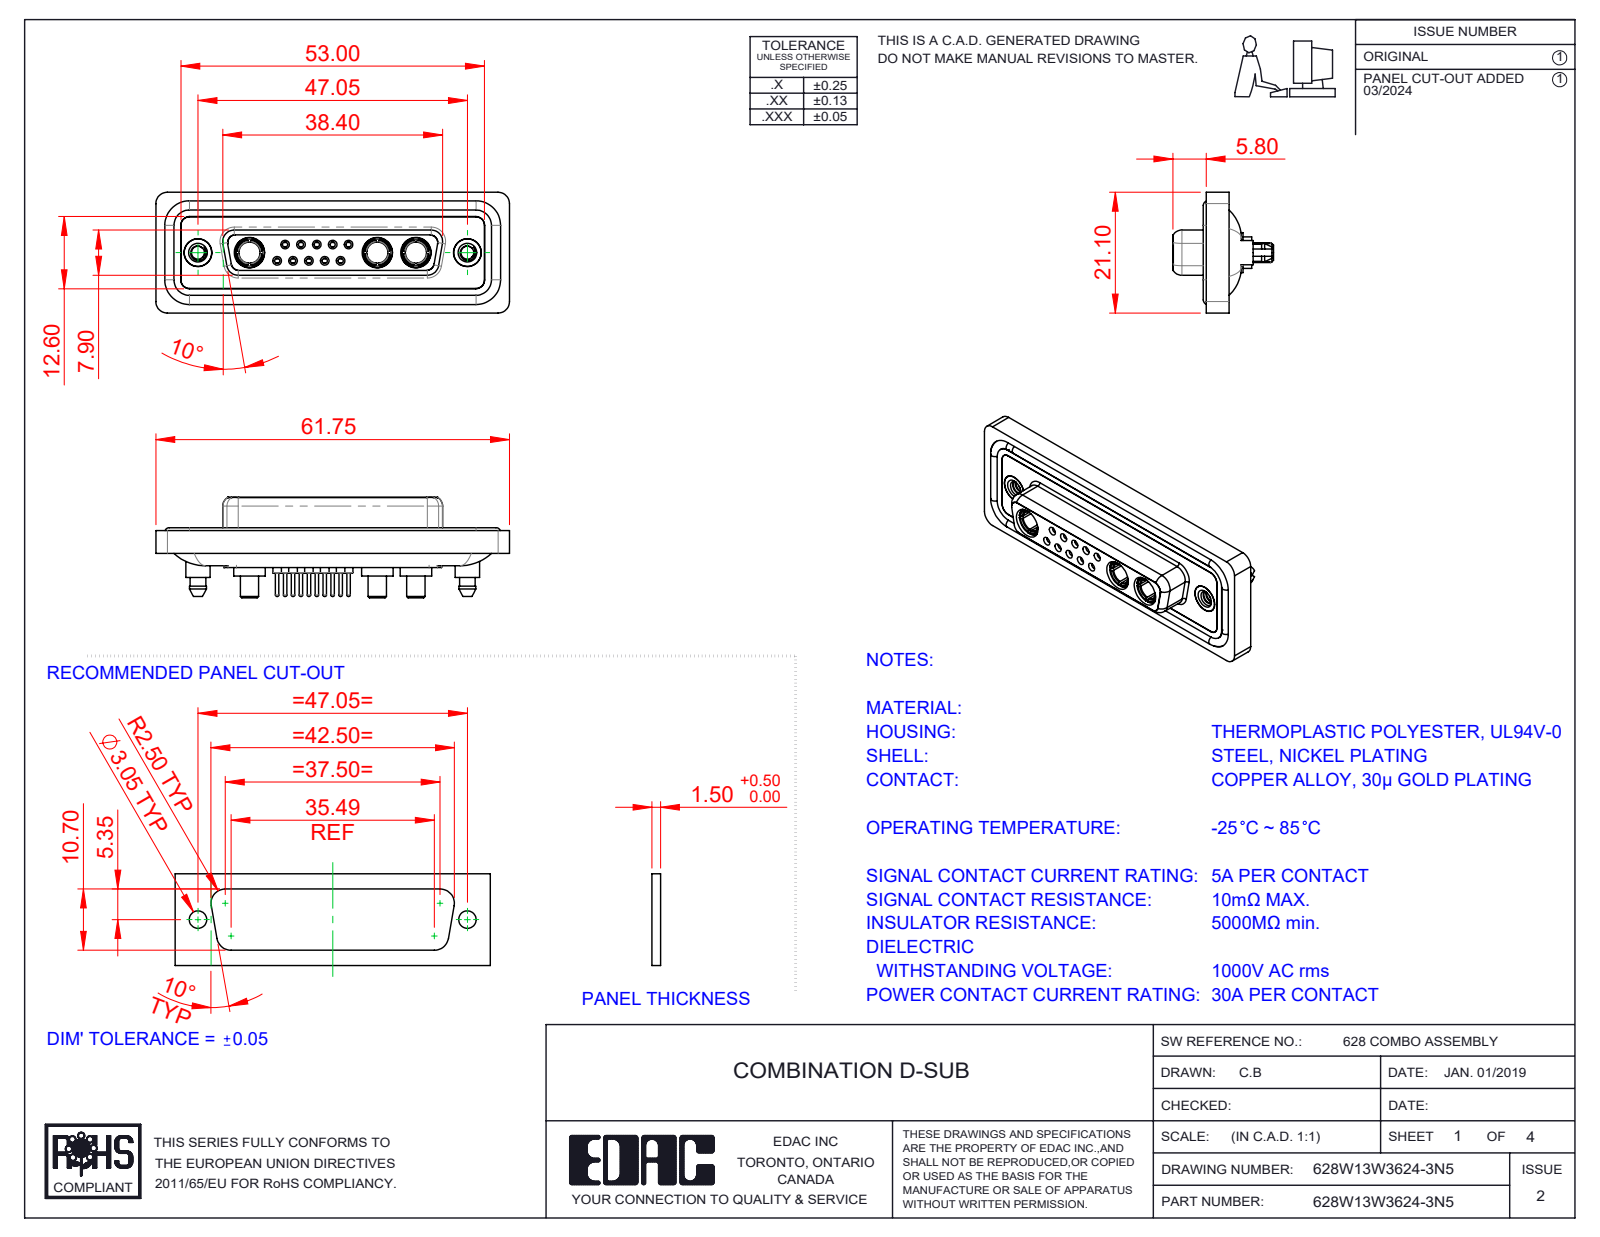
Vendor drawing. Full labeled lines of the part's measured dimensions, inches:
Part name (STEP PRODUCT): 628W13W3624-3N5; 628Combo Waterproof Housing_25 Contacts; 628Combo Contact Row 1_24; Power Socket_30A S (+5 more)
STEP written by: SolidWorks 2023 (CONFIG_CONTROL_DESIGN)
Units: inches
Bodies: 23 solids, 1208 faces (358 planar, 479 cylindrical, 371 other)
Overall size (bounding box): 2.431 × 0.831 × 0.691
Volume: 0.514 in³ · Surface area: 21.79 in²
Round holes (diameter × count): ⌀0.035 ×10, ⌀0.043 ×10, ⌀0.059 ×10, ⌀0.079 ×10, ⌀0.063 ×5, ⌀0.067 ×5, ⌀0.191 ×5, ⌀0.146 ×3, ⌀0.209 ×3, ⌀0.089 ×2, ⌀0.157 ×2, ⌀0.159 ×2
Round bosses / shafts (diameter × count): ⌀0.087 ×10, ⌀0.024 ×10, ⌀0.063 ×9, ⌀0.217 ×3, ⌀0.205 ×3, ⌀0.195 ×3, ⌀0.187 ×3, ⌀0.148 ×3
Partial cylindrical surfaces — rounded edges, fillets, slot ends (radius × count): R0.059 ×24, R0.079 ×18, R0.063 ×10, R0.053 ×8, R0.01 ×4, R0.02 ×4, R0.024 ×4, R0.026 ×4
Main face-to-face distances: 0.016, 0.071, 0.293, 0.222, 0.02, 0.26, 0.278, 0.063, 0.114, 0.043
Hole centre spacings: 0.124, 0.109, 0.198, 0.198, 0.218, 0.327, 0.295, 0.109
